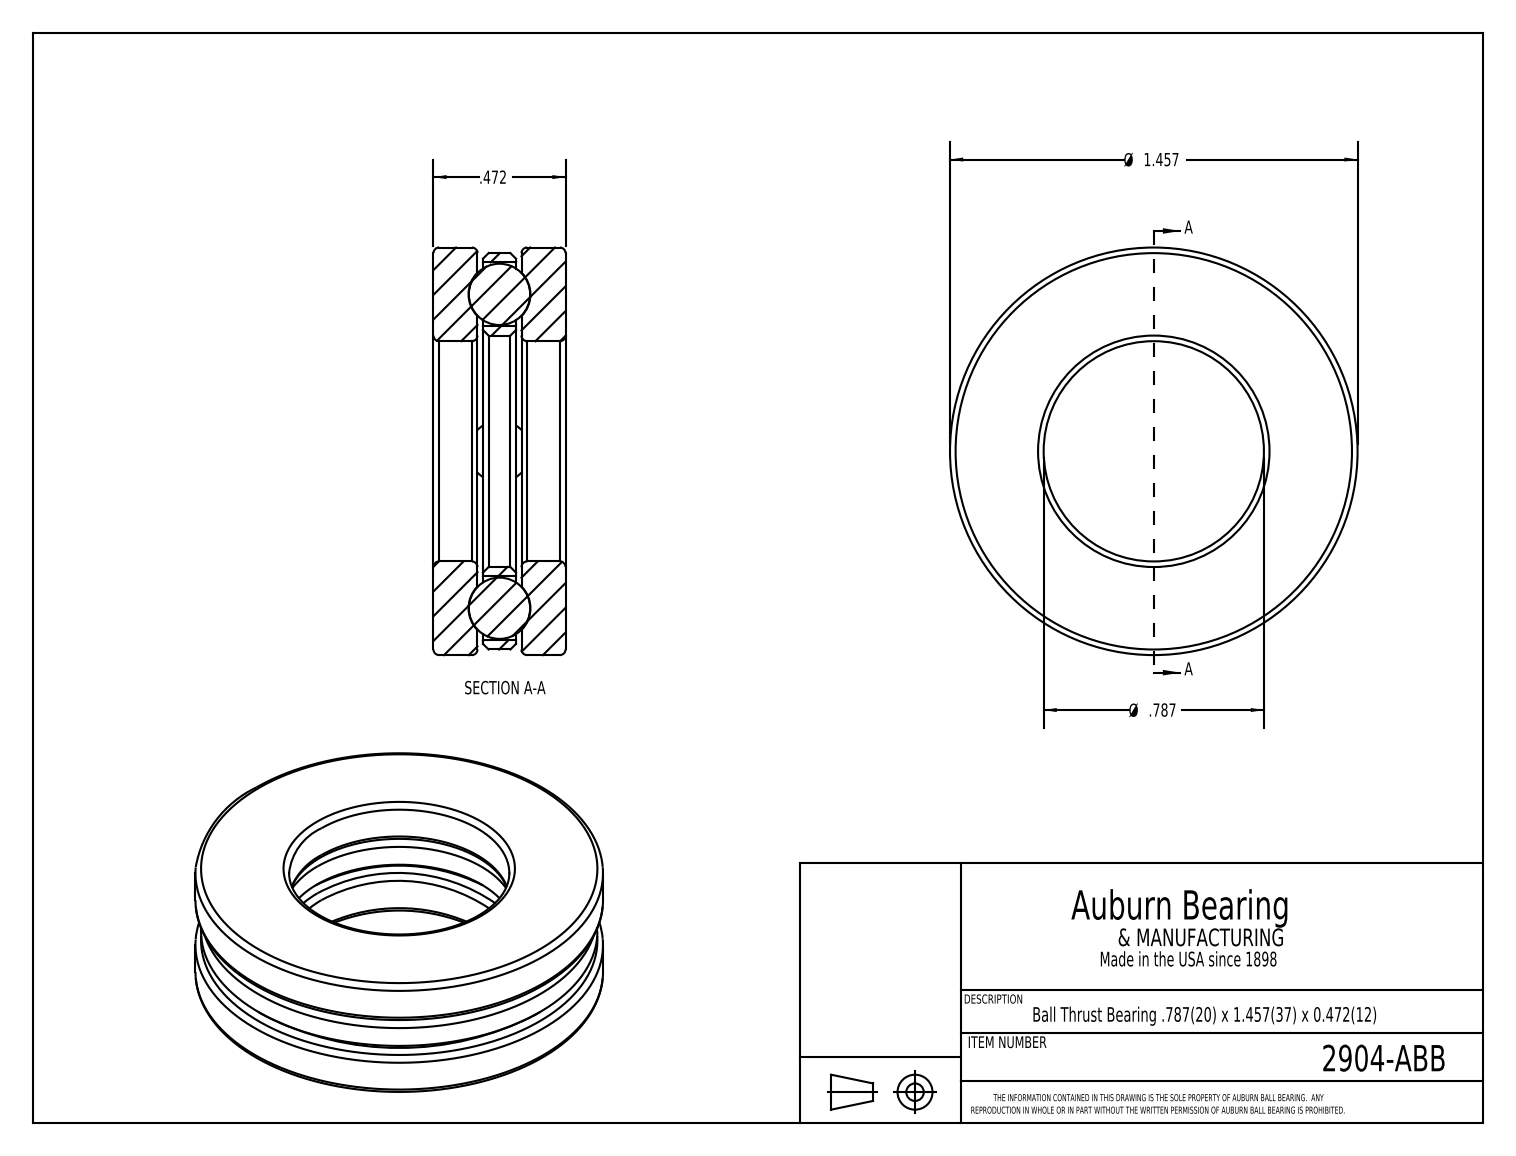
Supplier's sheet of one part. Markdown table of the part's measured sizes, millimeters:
| quantity | value |
| --- | --- |
| part name | 2904-ABB |
| STEP written by | SolidWorks 2017 (CONFIG_CONTROL_DESIGN) |
| units | millimeters |
| bodies | 7 solids, 36 faces (8 planar, 10 cylindrical, 18 other) |
| overall size | 37 × 37 × 12 |
| volume | 7 690 mm³ |
| surface area | 6 561 mm² |
| round holes (diameter × count) | 5.8 × 4, 20 × 1, 21 × 1 |
| round bosses / shafts (diameter × count) | 37 × 1, 36 × 1 |
| main face-to-face distances | 4.5, 7.5, 12, 4, 8, 0.5, 3.5, 3, 4 |
| hole center spacings | 14.2, 20.1, 28.5 |
